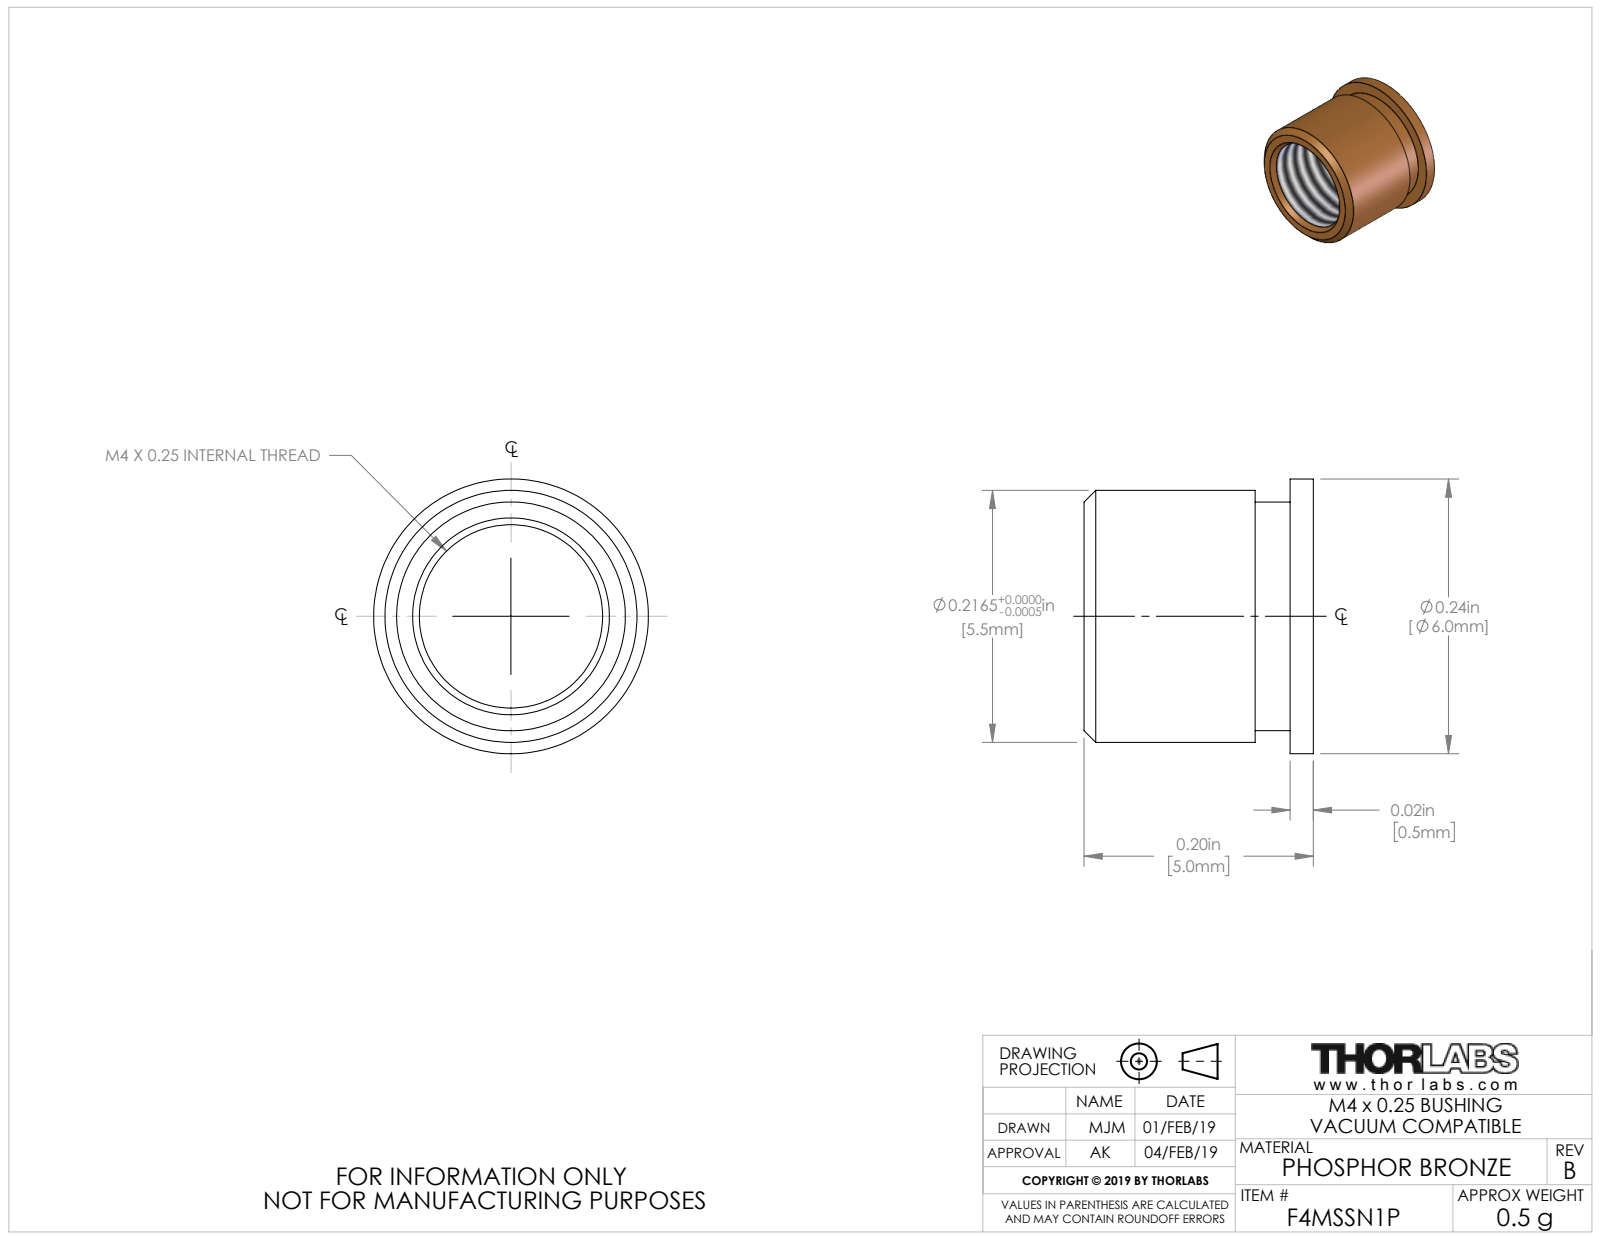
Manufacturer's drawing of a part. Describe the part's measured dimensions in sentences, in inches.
The part is named "TTN175562-E0W". Its 3-D file was written by "SolidWorks 2018 (AUTOMOTIVE_DESIGN)". It is 1 solid with 18 faces: 4 planar, 8 cylindrical and 6 other. Overall it measures 0.236 by 0.236 by 0.197 inches. Its volume is 0.003 cubic inches and its surface area 0.284 square inches. Round holes: 1 of diameter 0.157. Round bosses or shafts: 1 of diameter 0.236, 1 of diameter 0.217, 1 of diameter 0.197. The main face-to-face distances are 0.02, 0.197, 0.177, 0.05, 0.03, 0.147.
